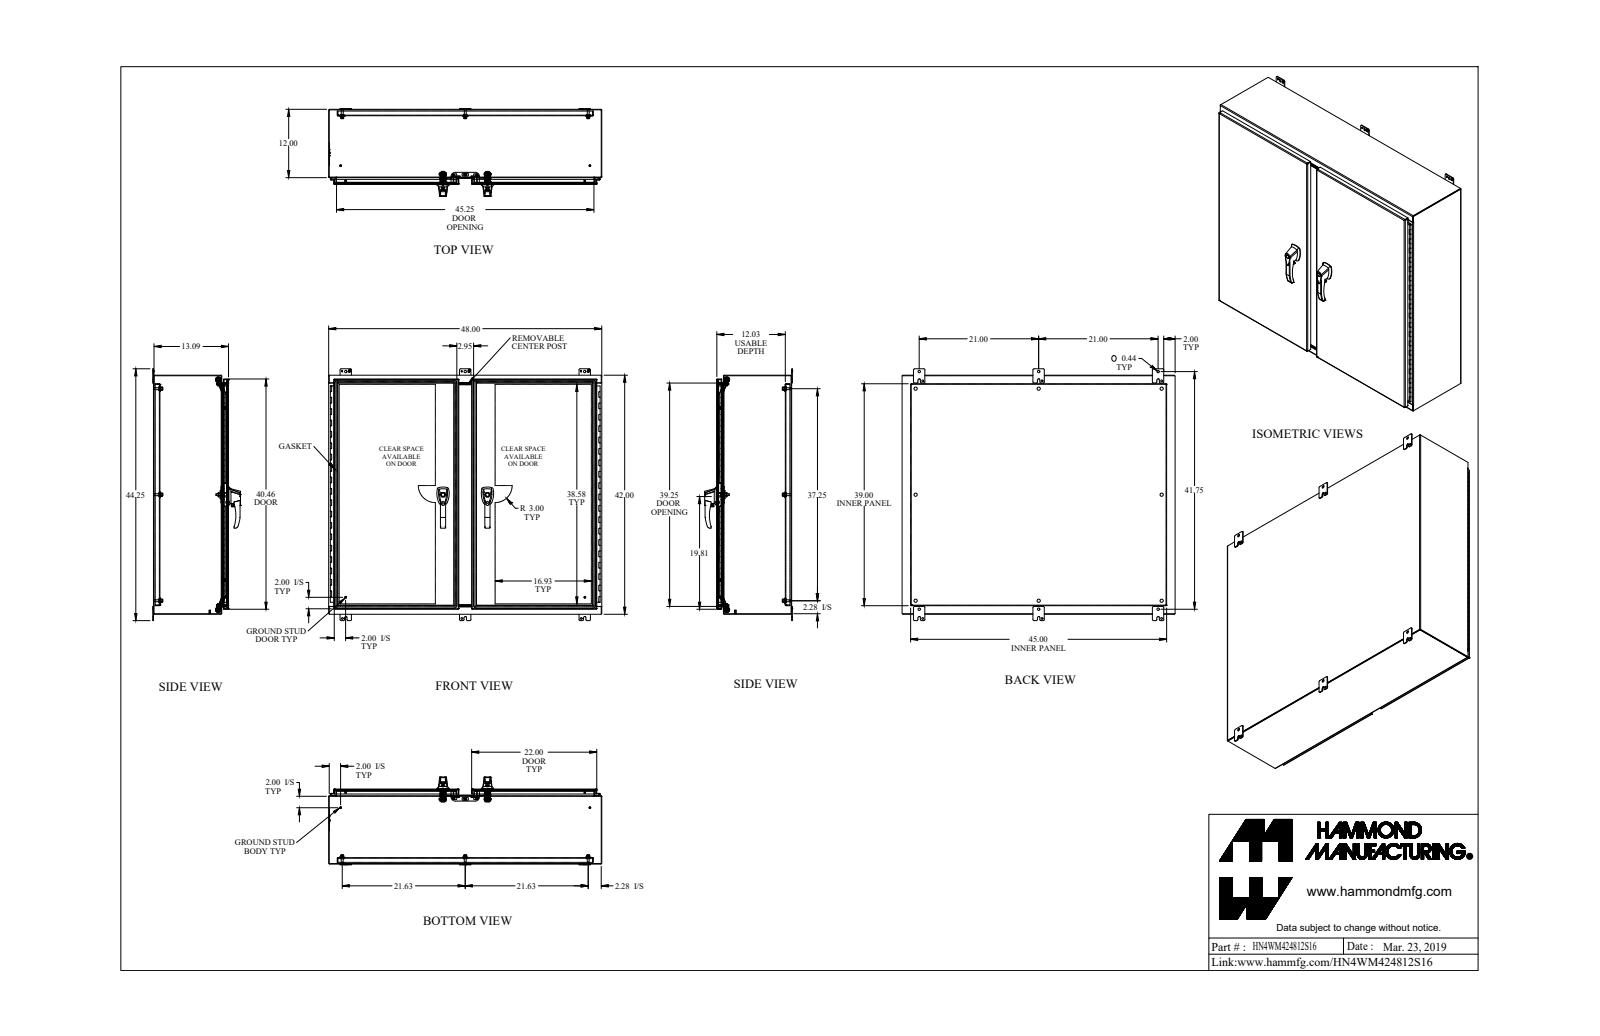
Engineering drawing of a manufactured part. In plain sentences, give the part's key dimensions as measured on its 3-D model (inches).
The part is named "HN4WM424812S16". Its 3-D file was written by "SolidWorks 2018 (AUTOMOTIVE_DESIGN)". It is 114 solids with 3076 faces: 1445 planar, 1355 cylindrical and 276 other. Overall it measures 48 by 44.25 by 15.425 inches. Its volume is 906 cubic inches and its surface area 19 057 square inches. Round holes: 14 of diameter 0.304, 8 of diameter 0.307, 8 of diameter 0.563, 6 of diameter 0.313, 6 of diameter 0.445, 5 of diameter 0.25, 4 of diameter 0.281, 4 of diameter 0.313, 4 of diameter 0.39, 3 of diameter 0.201, 3 of diameter 0.437, 2 of diameter 0.11. Round bosses or shafts: 10 of diameter 1, 8 of diameter 0.65, 8 of diameter 0.375, 8 of diameter 0.332, 4 of diameter 0.75, 4 of diameter 0.625, 4 of diameter 0.44, 4 of diameter 0.37. Partial cylindrical surfaces (rounded edges, fillets, slot ends): 32 of radius 0.018, 31 of radius 0.125, 28 of radius 0.188, 26 of radius 0.25, 21 of radius 0.048, 21 of radius 0.143, 20 of radius 0.06, 17 of radius 0.5. The main face-to-face distances are 0.095, 1.032, 0.095, 13.09, 12.995, 13.185, 13.09, 1.127, 11.963, 12.058. The hole center spacings are 6, 46.508, 12, 47.655, 18, 49.508, 21.625, 46.12.
